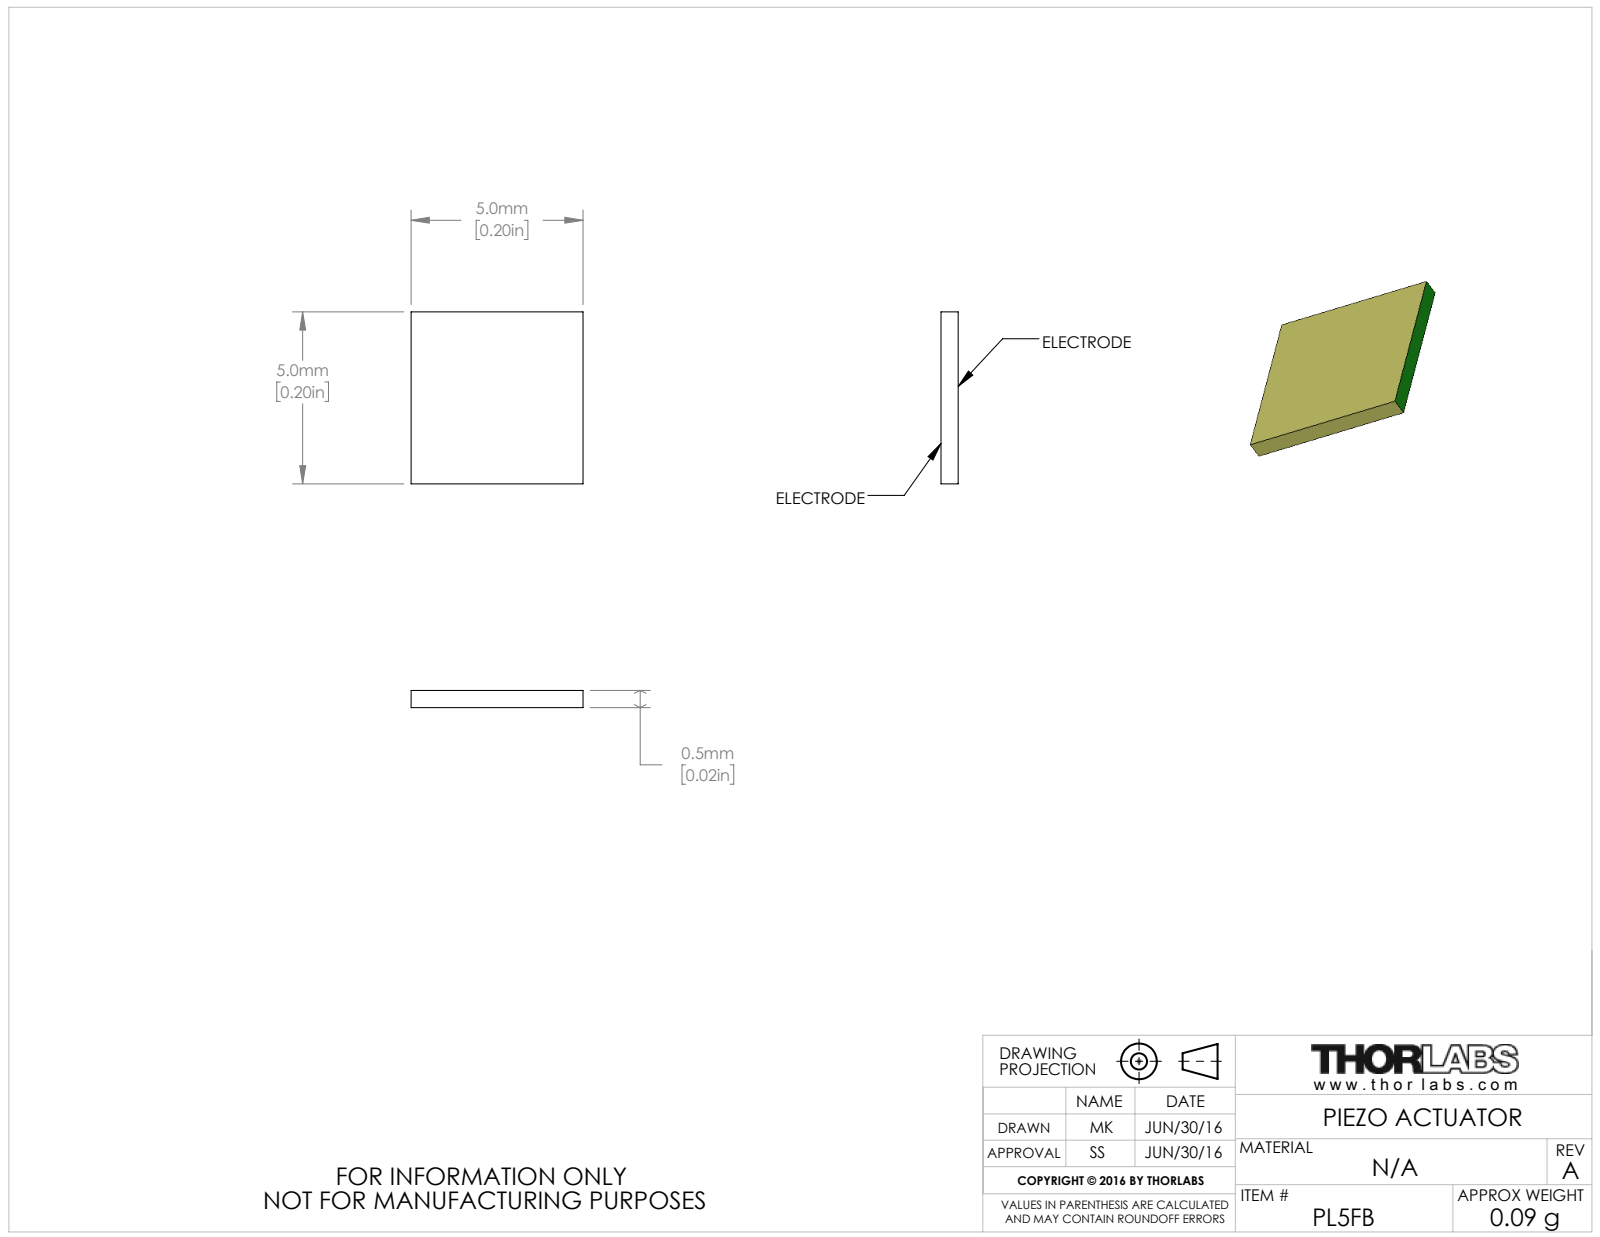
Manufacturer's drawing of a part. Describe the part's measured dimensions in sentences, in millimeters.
The part is named "CTN009238". Its 3-D file was written by "SolidWorks 2016 (AUTOMOTIVE_DESIGN)". It is 1 solid with 6 faces: 6 planar, 0 cylindrical and 0 other. Overall it measures 5 by 5 by 0.5 millimeters. Its volume is 12 cubic millimeters and its surface area 60 square millimeters. The main face-to-face distances are 0.5, 5.
